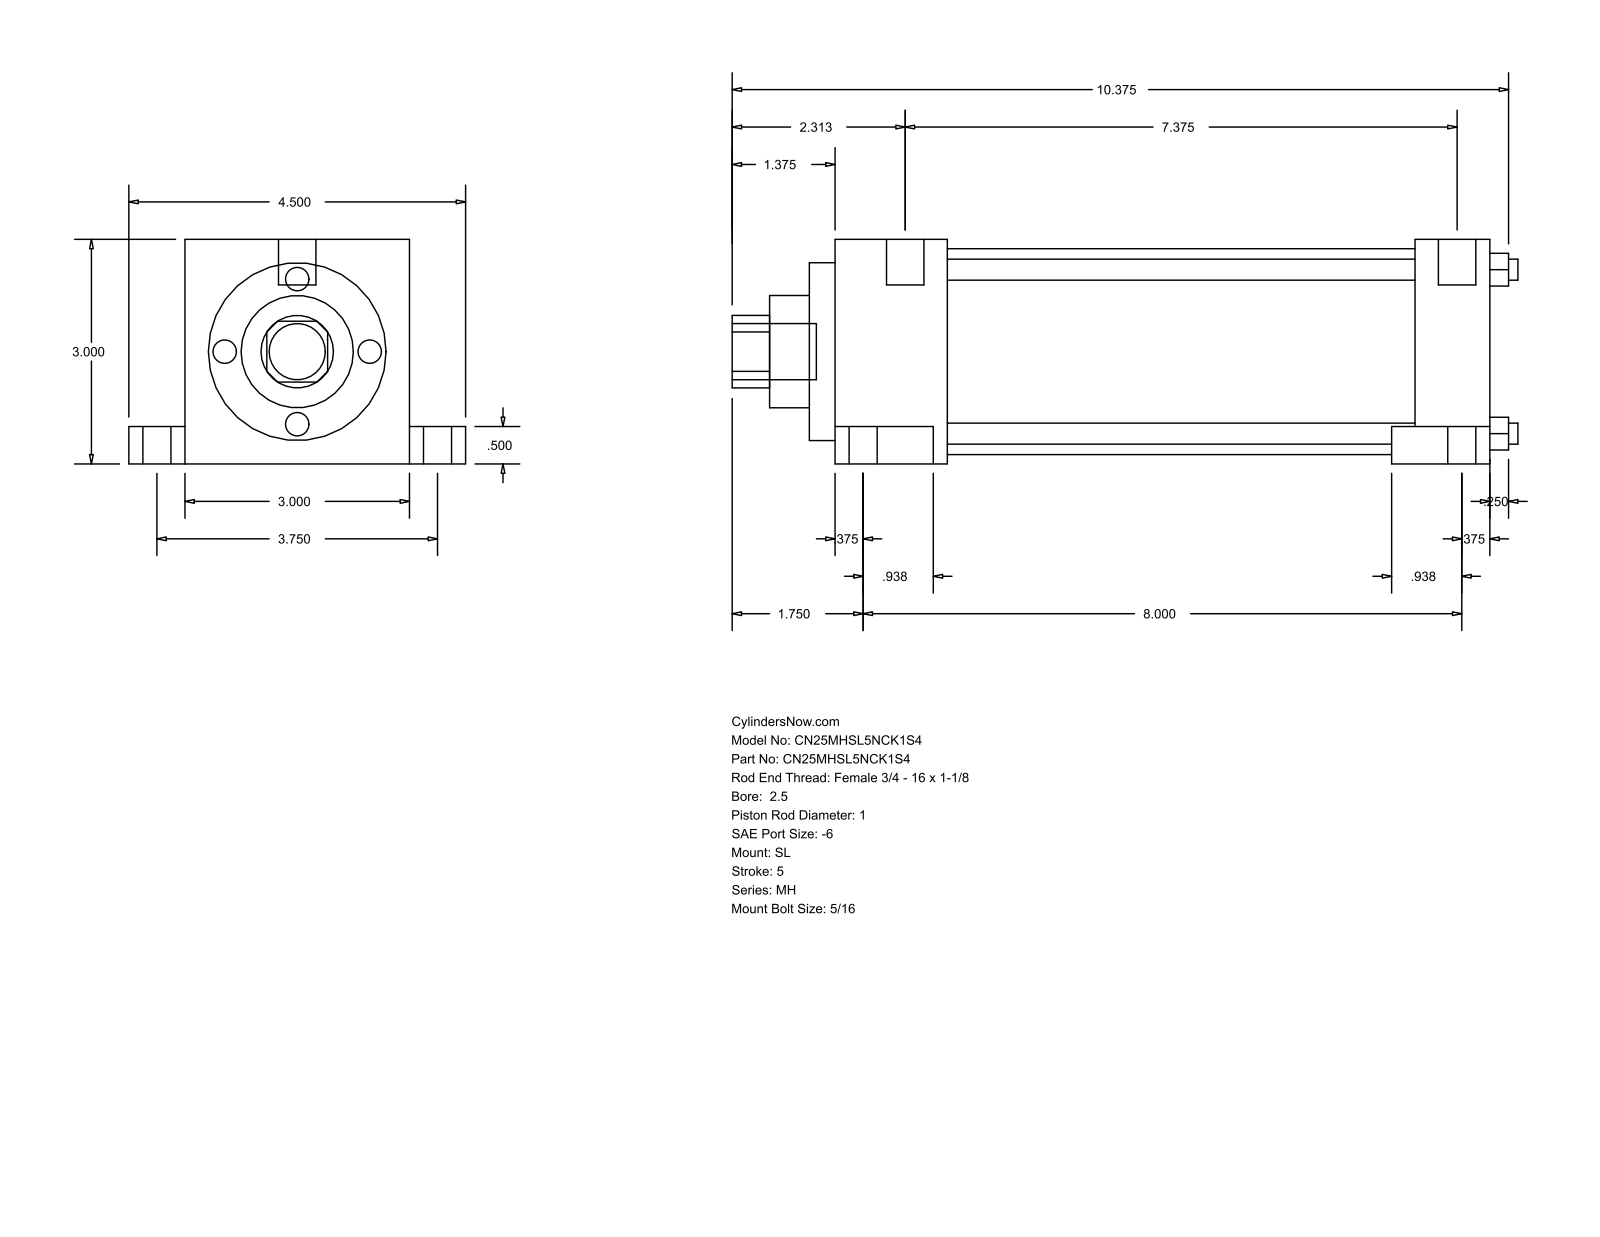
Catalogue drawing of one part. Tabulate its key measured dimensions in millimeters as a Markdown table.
| quantity | value |
| --- | --- |
| part name | MH_SL__0250_1 |
| STEP written by | GSSL Pune (CONFIG_CONTROL_DESIGN) |
| units | millimeters |
| bodies | 0 solids, 86 faces (61 planar, 25 cylindrical, 0 other) |
| overall size | 266.7 × 114.3 × 76.2 |
| round holes (diameter × count) | 7.14 × 4, 25.4 × 1, 38.1 × 1, 60.33 × 1, 69.85 × 1 |
| round bosses / shafts (diameter × count) | 15.88 × 2, 9.53 × 2, 5.56 × 2, 19.05 × 1, 12.7 × 1 |
| partial cylindrical surfaces (radius × count) | 12.29 × 1 |
| main face-to-face distances | 76.2, 25.4, 205.59, 230.99, 12.7, 63.5, 19.05, 95.25, 13.49, 219.08 |
| hole center spacings | 39.33, 55.62, 78.66 |
